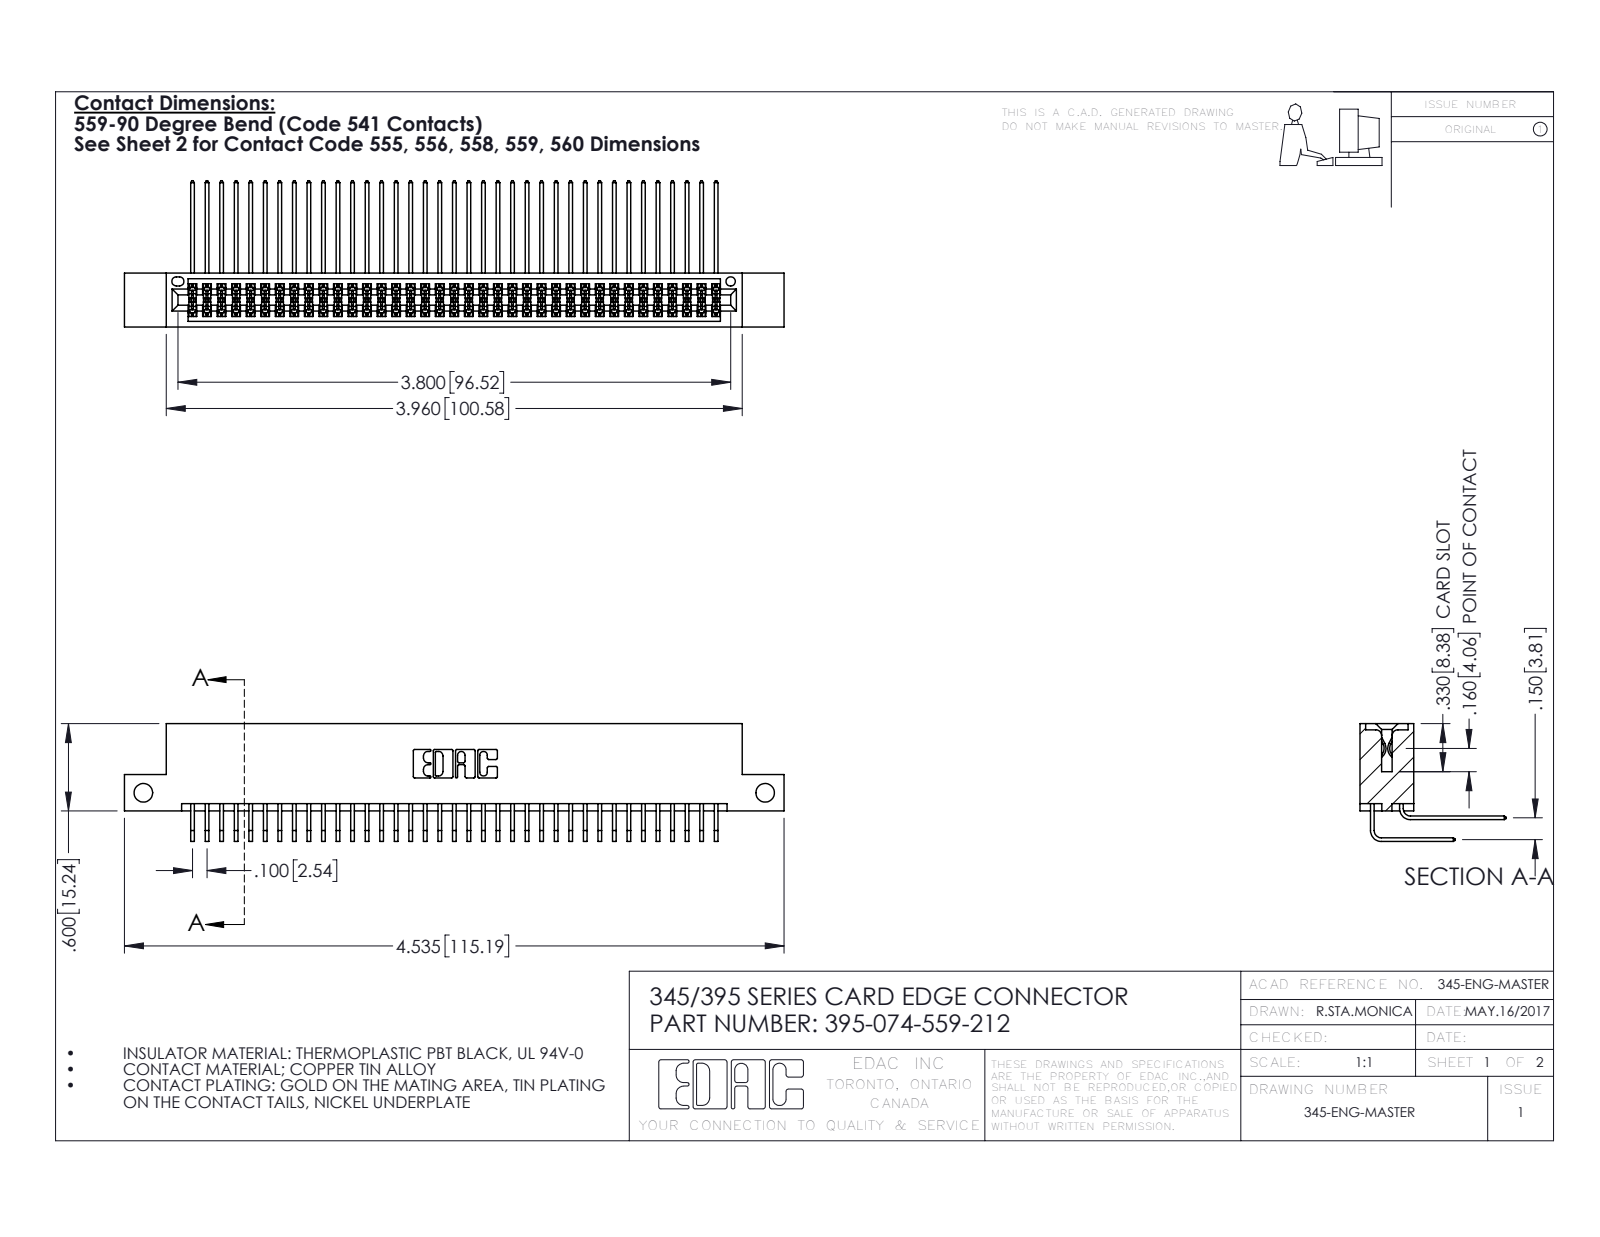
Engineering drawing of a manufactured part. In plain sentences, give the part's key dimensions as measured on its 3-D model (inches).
The part is named "345 Part_Flush Mounting Lugs - Side Mount; 345-292-001_558 559 Tail - 1; 395-074-559-212; 345-292-001_559 Tail - 2". Its 3-D file was written by "SolidWorks 2016 (CONFIG_CONTROL_DESIGN)". It is 75 solids with 3974 faces: 2670 planar, 1304 cylindrical and 0 other. Overall it measures 4.535 by 1.005 by 0.809 inches. Its volume is 0.701 cubic inches and its surface area 29.06 square inches. Round holes: 2 of diameter 0.128, 1 of diameter 0.064. Partial cylindrical surfaces (rounded edges, fillets, slot ends): 112 of radius 0.006, 22 of radius 0.01, 6 of radius 0.007, 6 of radius 0.031, 3 of radius 0.026, 2 of radius 0.014, 2 of radius 0.019, 2 of radius 0.022. The main face-to-face distances are 0.072, 0.298, 0.2, 0.37, 0.098, 0.272, 0.025, 0.225, 0.175, 0.15. The hole center spacings are 4.275.
